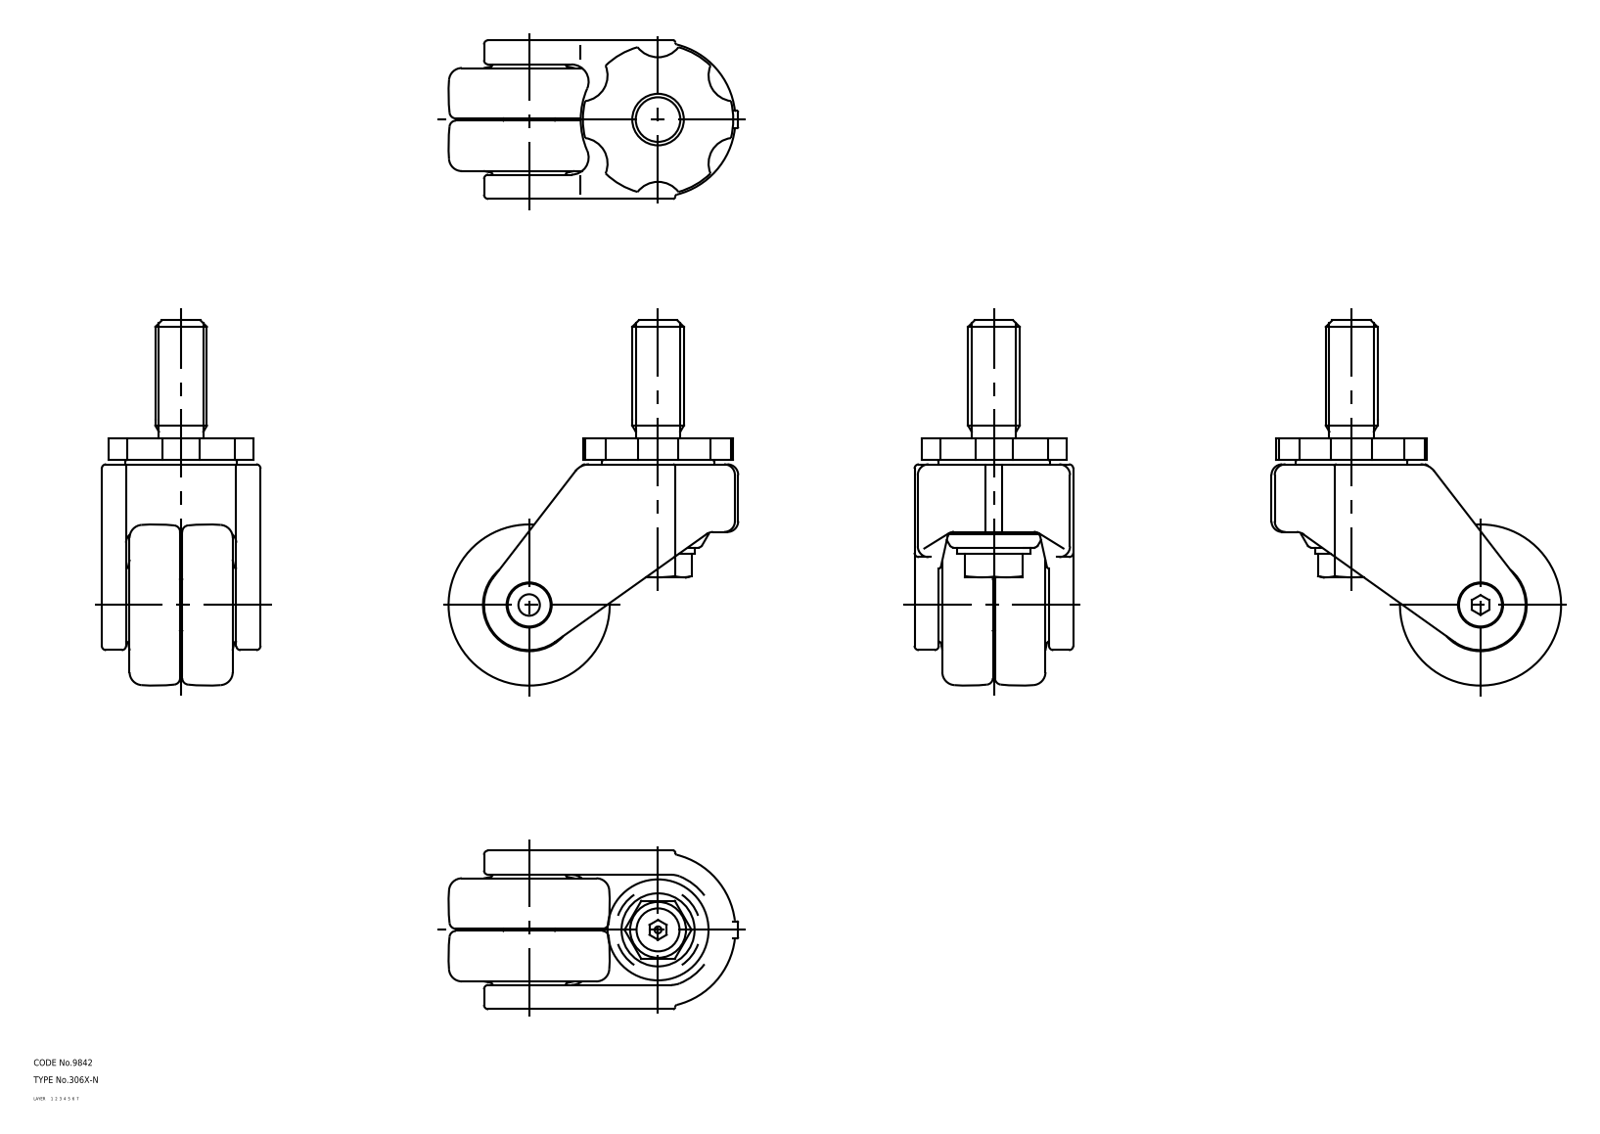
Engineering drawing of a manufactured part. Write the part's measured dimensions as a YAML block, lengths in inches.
part_name: "wheel; main shaft; axle; No_306X_N_24109_36"
step_written_by: "CADfix (AUTOMOTIVE_DESIGN)"
units: inches
bodies: {solids: 4, faces: 246, planar: 0, cylindrical: 0, other: 246}
overall_size: [6.693, 5.307, 2.909]
volume: 31.35
surface_area: 137.6
